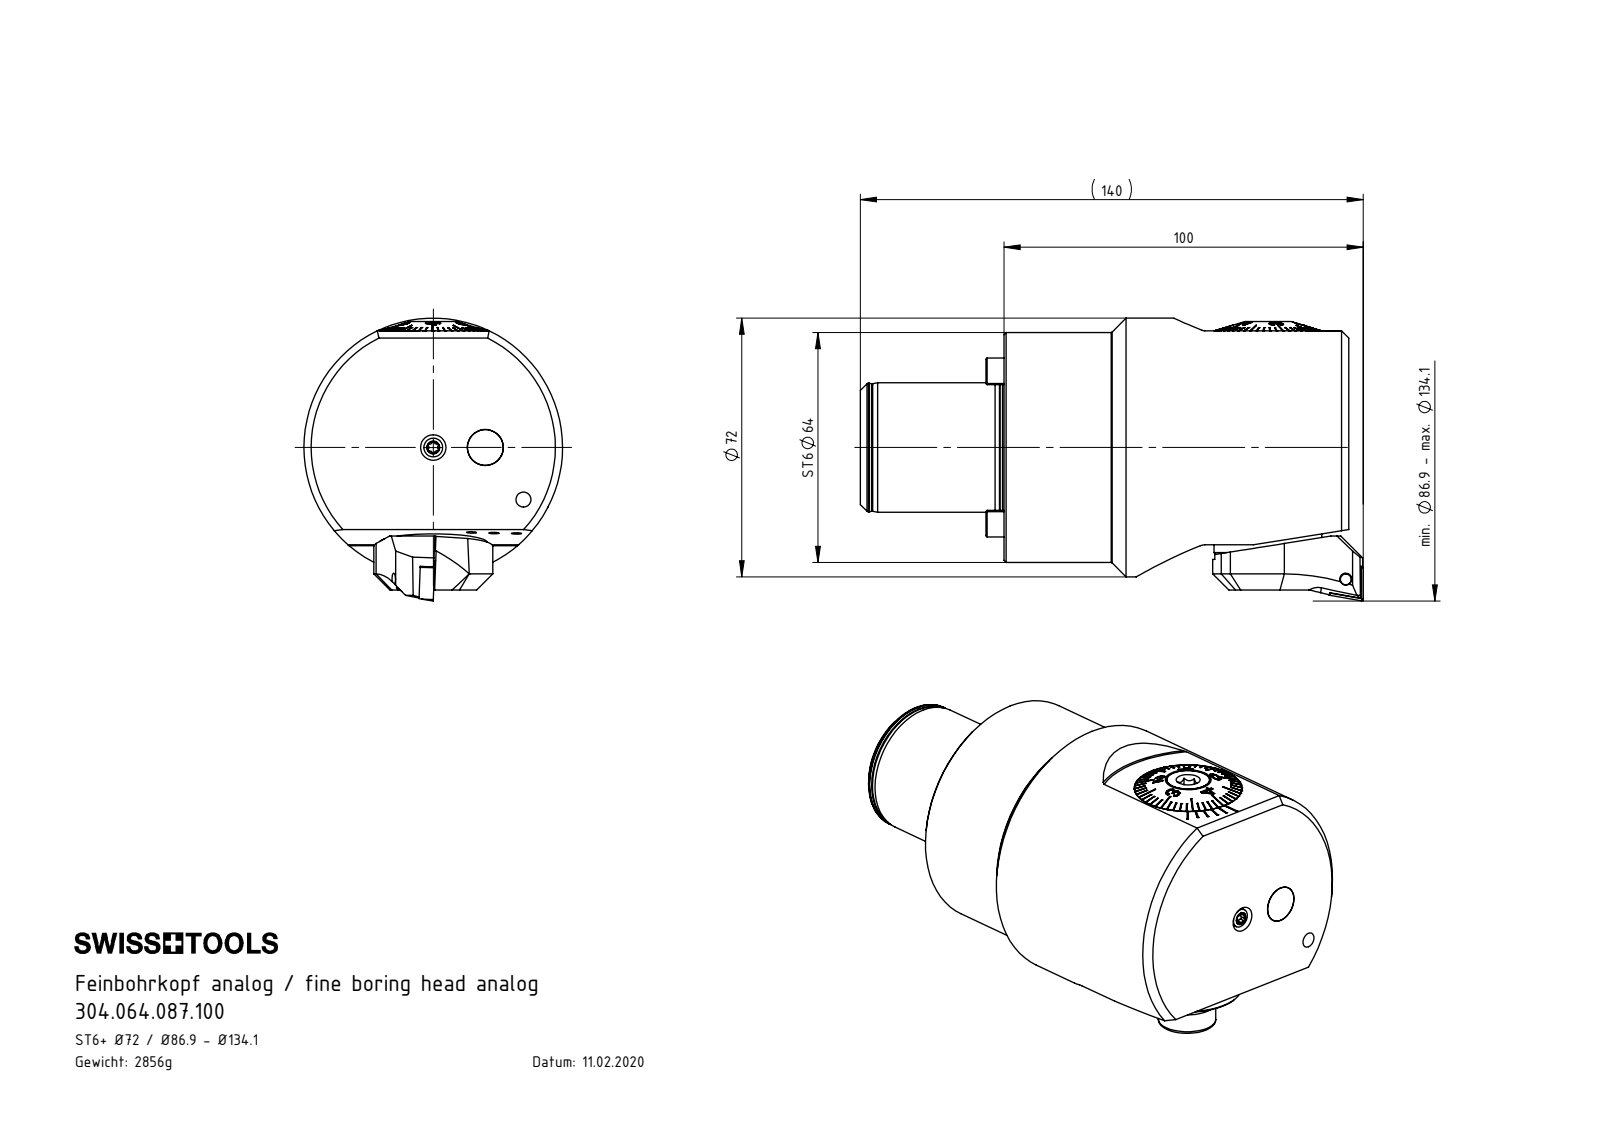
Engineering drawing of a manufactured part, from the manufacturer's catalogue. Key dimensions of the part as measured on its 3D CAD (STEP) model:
Part name (STEP PRODUCT): A55-BG2.011.016_D; CCMT09T304; A55-BG3.011.033_A_gekrzt; ST6-F72.K20.100_B (+8 more)
STEP written by: SolidWorks 2015 (CONFIG_CONTROL_DESIGN)
Units: millimetres
Bodies: 18 solids, 904 faces (330 planar, 194 cylindrical, 380 other)
Overall size (bounding box): 140 × 79.45 × 72
Volume: 400 670 mm³ · Surface area: 68 432 mm²
Round holes (diameter × count): ⌀3.3 ×9, ⌀5 ×3, ⌀8.5 ×3, ⌀4.2 ×1, ⌀4.4 ×1, ⌀6.1 ×1, ⌀8 ×1, ⌀10 ×1, ⌀11 ×1, ⌀11.75 ×1, ⌀12 ×1, ⌀12.4 ×1
Round bosses / shafts (diameter × count): ⌀10 ×2, ⌀5.25 ×2, ⌀4 ×2, ⌀72 ×1, ⌀36 ×1, ⌀35.8 ×1, ⌀35.3 ×1, ⌀29.98 ×1
Partial cylindrical surfaces — rounded edges, fillets, slot ends (radius × count): R0.34 ×12, R0.59 ×12, R0.5 ×8, R3.2 ×3, R5.47 ×2, R10 ×2, R18.05 ×2, R1 ×1
Main face-to-face distances: 96, 6.48, 2.5, 5.3, 1.18, 56.37, 61.67, 62.85, 59.17, 2.8
Hole centre spacings: 21.5, 25.93, 5.73, 5.86, 14.05, 14.5, 26, 26.14
